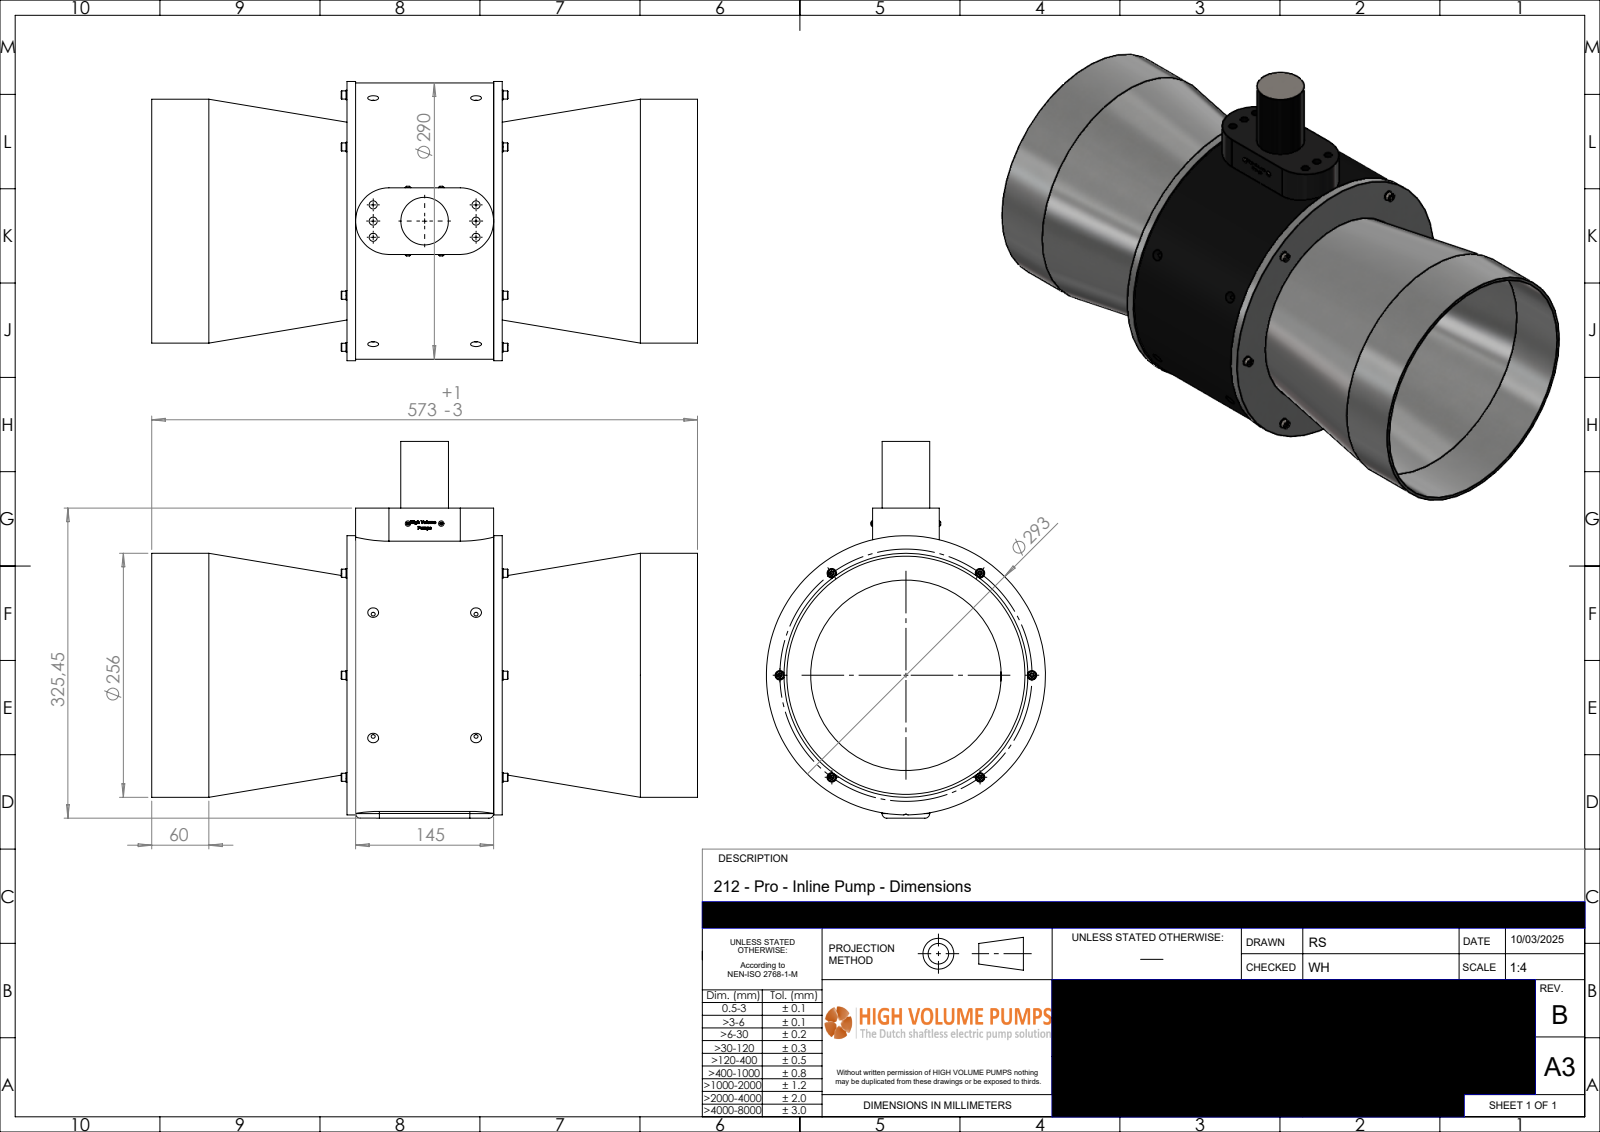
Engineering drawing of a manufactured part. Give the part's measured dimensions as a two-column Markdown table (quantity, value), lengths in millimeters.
| quantity | value |
| --- | --- |
| part name | P-212-530-rev-B-IP |
| STEP written by | SolidWorks 2024 (AUTOMOTIVE_DESIGN) |
| units | millimeters |
| bodies | 1 solid, 943 faces (550 planar, 107 cylindrical, 286 other) |
| overall size | 573.06 × 395.45 × 293 |
| volume | 6 455 000 mm³ |
| surface area | 993 093 mm² |
| round holes (diameter × count) | 5.6 × 6, 8.5 × 6, 4.2 × 4, 5.3 × 2, 209 × 1, 212 × 1, 250 × 1 |
| round bosses / shafts (diameter × count) | 5 × 8, 10 × 6, 8.5 × 6, 9.64 × 2, 5.7 × 2, 293 × 1, 290 × 1, 256 × 1 |
| partial cylindrical surfaces (radius × count) | 2 × 2, 5 × 2, 25 × 2, 35 × 2, 1 × 1 |
| main face-to-face distances | 163.06, 154.06, 9, 5, 325.45, 4, 205, 214, 359.06, 368.06 |
| hole center spacings | 108, 17, 109.33, 120.19, 132.37, 235.9, 34, 113.23 |
